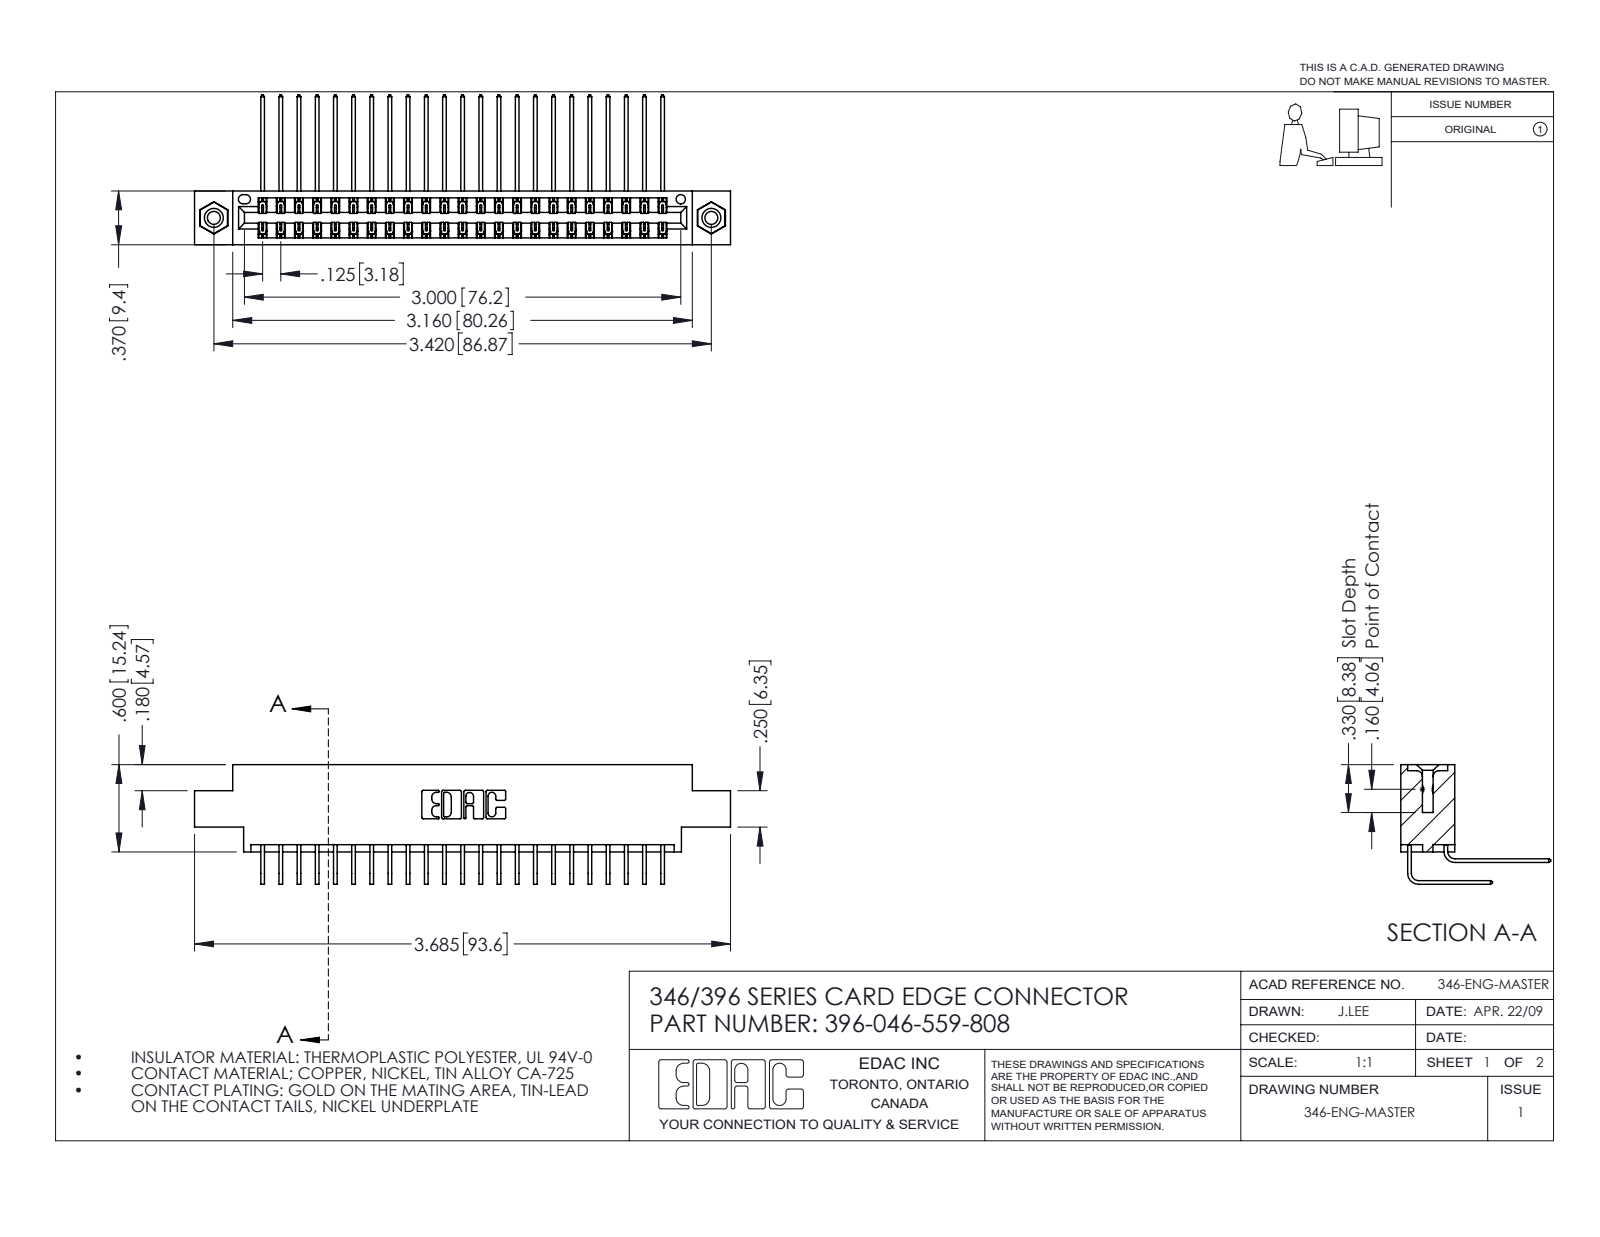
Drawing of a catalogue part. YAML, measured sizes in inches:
part_name: "345-250-001_345-250-003-102; 345-292-001_559 Tail - 2; 345-292-001_558 559 Tail - 1; 346 Part_0.170 Offset - 0.156 Dia-TI (+1 more)"
step_written_by: "SolidWorks 2016 (CONFIG_CONTROL_DESIGN)"
units: inches
bodies: {solids: 49, faces: 2670, planar: 1814, cylindrical: 840, other: 16}
overall_size: [3.685, 1.03, 0.823]
volume: 0.554
surface_area: 21.17
round_holes:
  - {diameter: 0.089, count: 2}
  - {diameter: 0.125, count: 2}
  - {diameter: 0.156, count: 2}
  - {diameter: 0.064, count: 1}
round_bosses_or_shafts:
  - {diameter: 0.155, count: 2}
partial_cylinders:
  - {radius: 0.006, count: 69}
  - {radius: 0.01, count: 22}
  - {radius: 0.007, count: 6}
  - {radius: 0.031, count: 6}
  - {radius: 0.026, count: 3}
  - {radius: 0.014, count: 2}
  - {radius: 0.022, count: 2}
  - {radius: 0.024, count: 2}
face_to_face_distances: [0.048, 0.322, 0.025, 0.37, 0.25, 0.072, 0.298, 0.275, 0.222, 0.148]
hole_center_spacings: [0.246, 3.212, 3.42]
